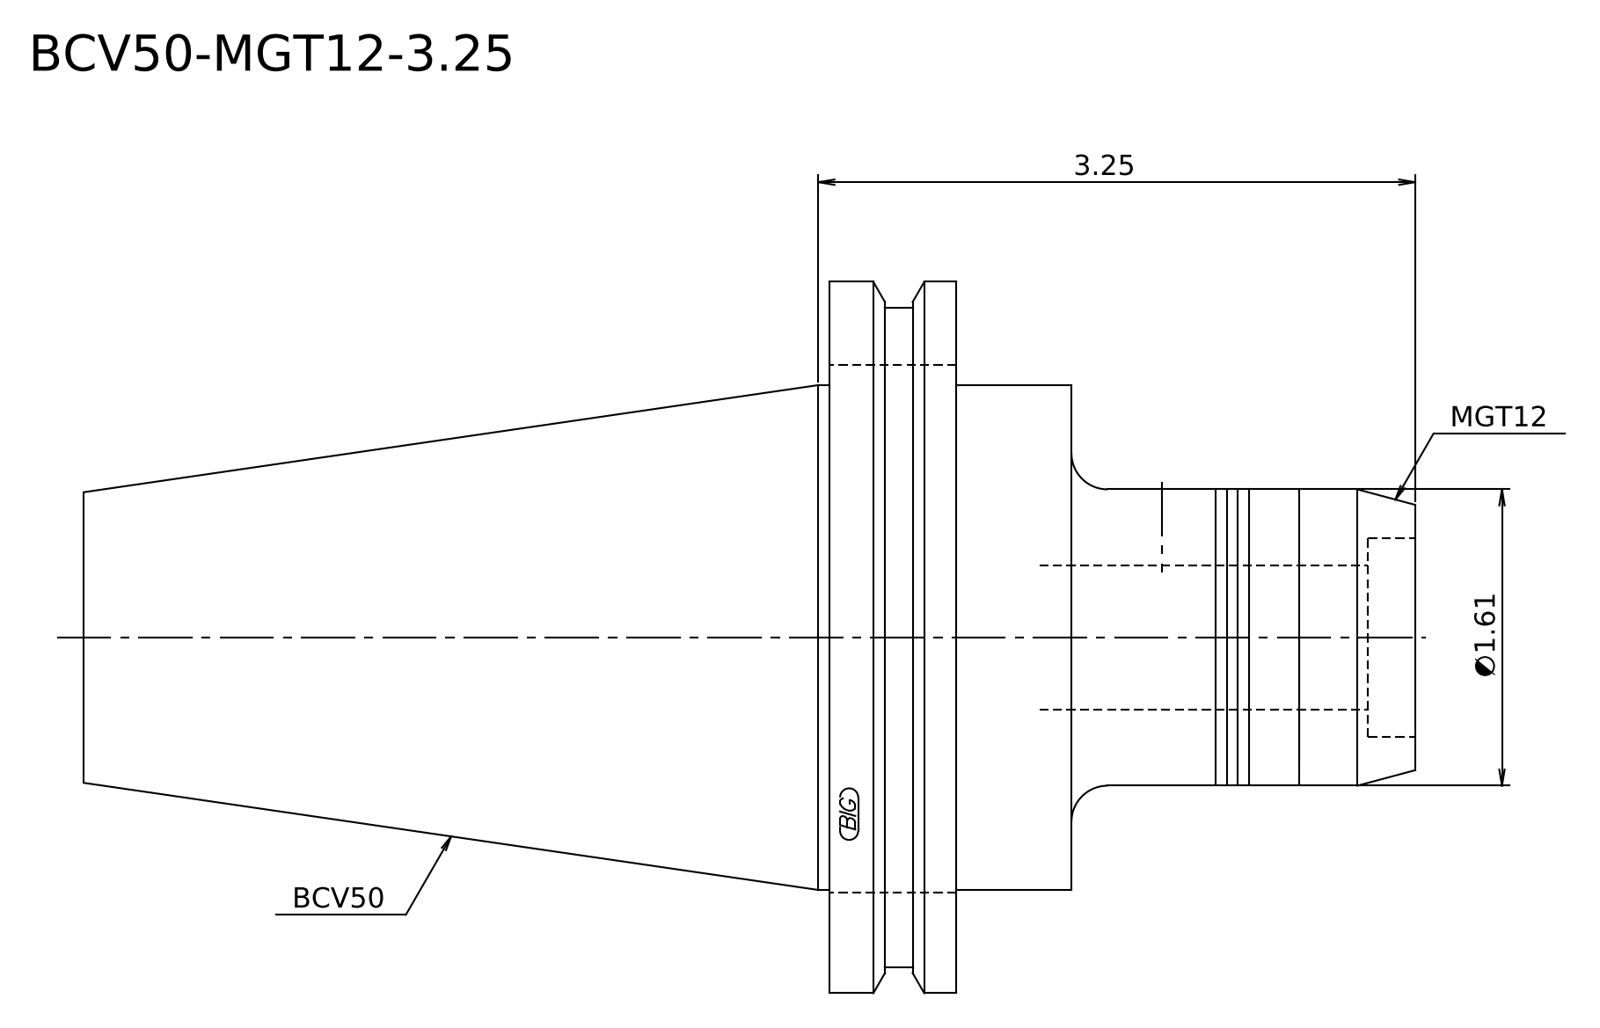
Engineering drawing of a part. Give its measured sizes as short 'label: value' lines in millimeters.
written by: Kubotek KeyCreator 2011 V10.0.2 (22737) (automotive_design)
unit: mm
bodies: 1 solid, 18 faces (7 planar, 6 cylindrical, 5 other)
size: 184.15 × 98.42 × 98.42
volume: 505 931 mm³; area: 46 468 mm²
bosses: 1× ⌀98.42, 1× ⌀91.29, 1× ⌀69.85, 1× ⌀41
face distances: 17.55, 15.95, 33.5, 136.6, 120.65, 103.1, 47.55, 63.5, 81.05, 184.15
